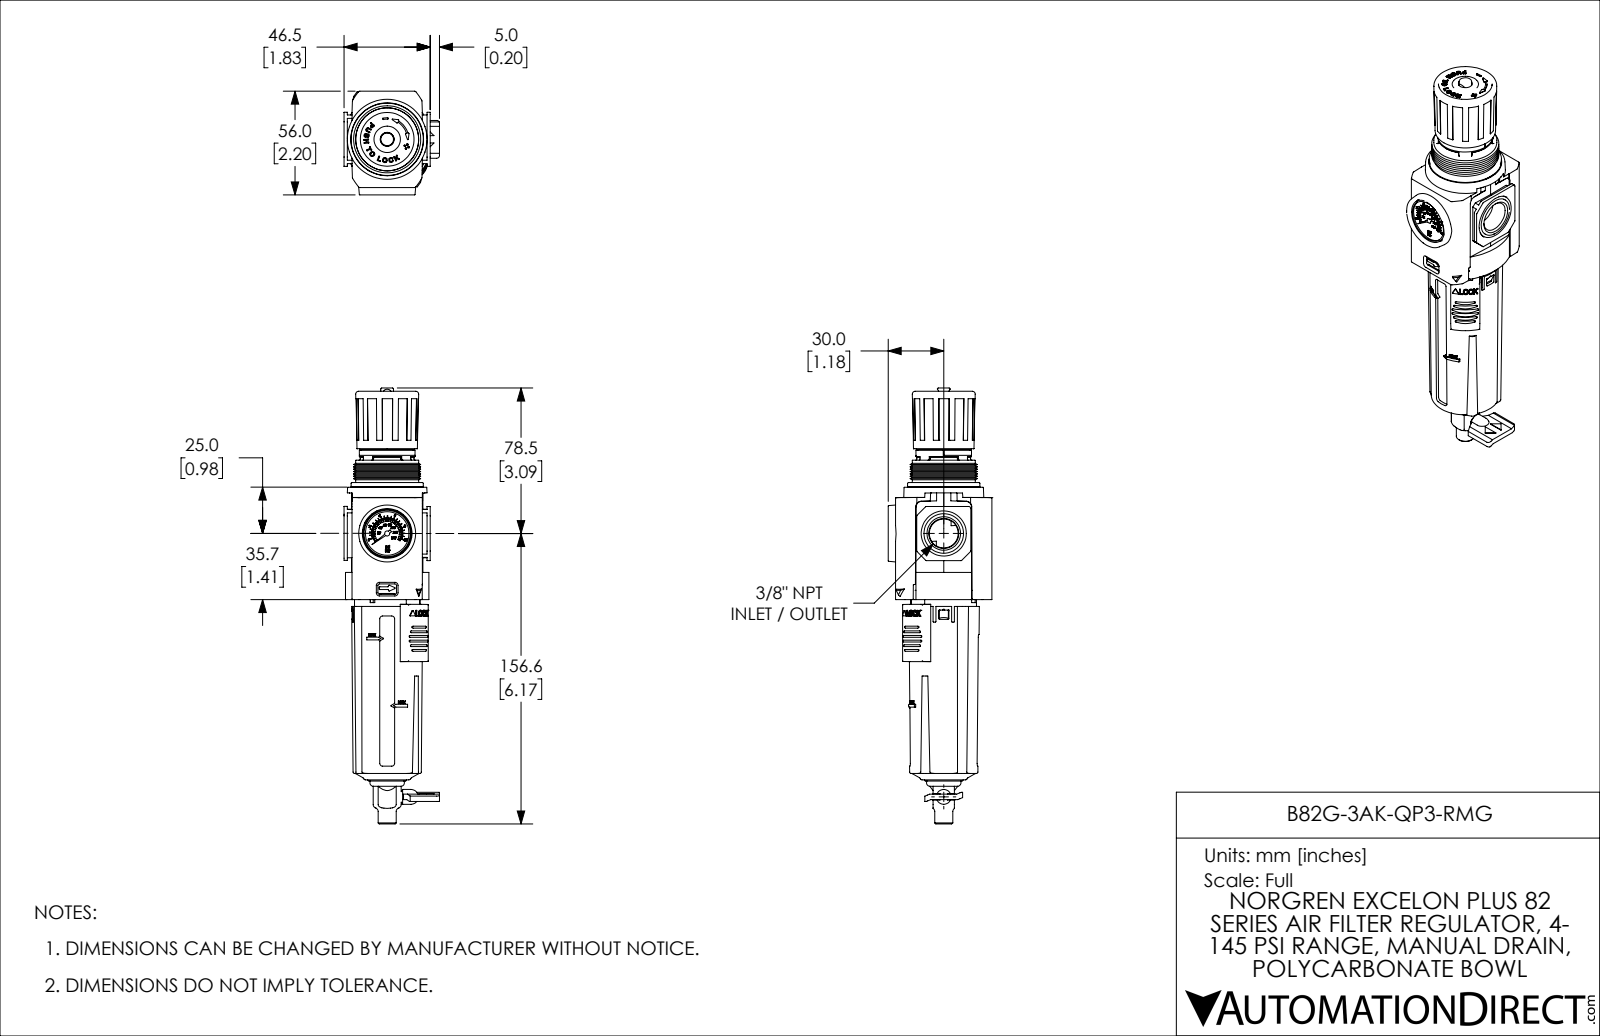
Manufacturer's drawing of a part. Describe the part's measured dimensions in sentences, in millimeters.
The part is named "B82G-3AK-QP3-RMG". Its 3-D file was written by "SolidWorks 2021 (CONFIG_CONTROL_DESIGN)". It is 8 solids with 2685 faces: 1044 planar, 1230 cylindrical and 411 other. Overall it measures 235.1 by 56 by 51.5 millimeters. Its volume is 287 800 cubic millimeters and its surface area 75 100 square millimeters. Round holes: 4 of diameter 2.5, 2 of diameter 3.5, 1 of diameter 3.3, 1 of diameter 5, 1 of diameter 6, 1 of diameter 6.4, 1 of diameter 16, 1 of diameter 23.5, 1 of diameter 28, 1 of diameter 34.4. Round bosses or shafts: 2 of diameter 5.7, 2 of diameter 3, 1 of diameter 39, 1 of diameter 35.3, 1 of diameter 34.4, 1 of diameter 34, 1 of diameter 32.8, 1 of diameter 31.9. Partial cylindrical surfaces (rounded edges, fillets, slot ends): 55 of radius 0.5, 30 of radius 1, 25 of radius 0.2, 20 of radius 0.8, 19 of radius 0.2, 15 of radius 0.3, 12 of radius 0.3, 12 of radius 0.3. The main face-to-face distances are 1.5, 50.5, 43, 9, 41.5, 7.5, 36, 37.5, 6, 4.6. The hole center spacings are 16, 27.7, 32, 68.7, 84.5, 75.3.
